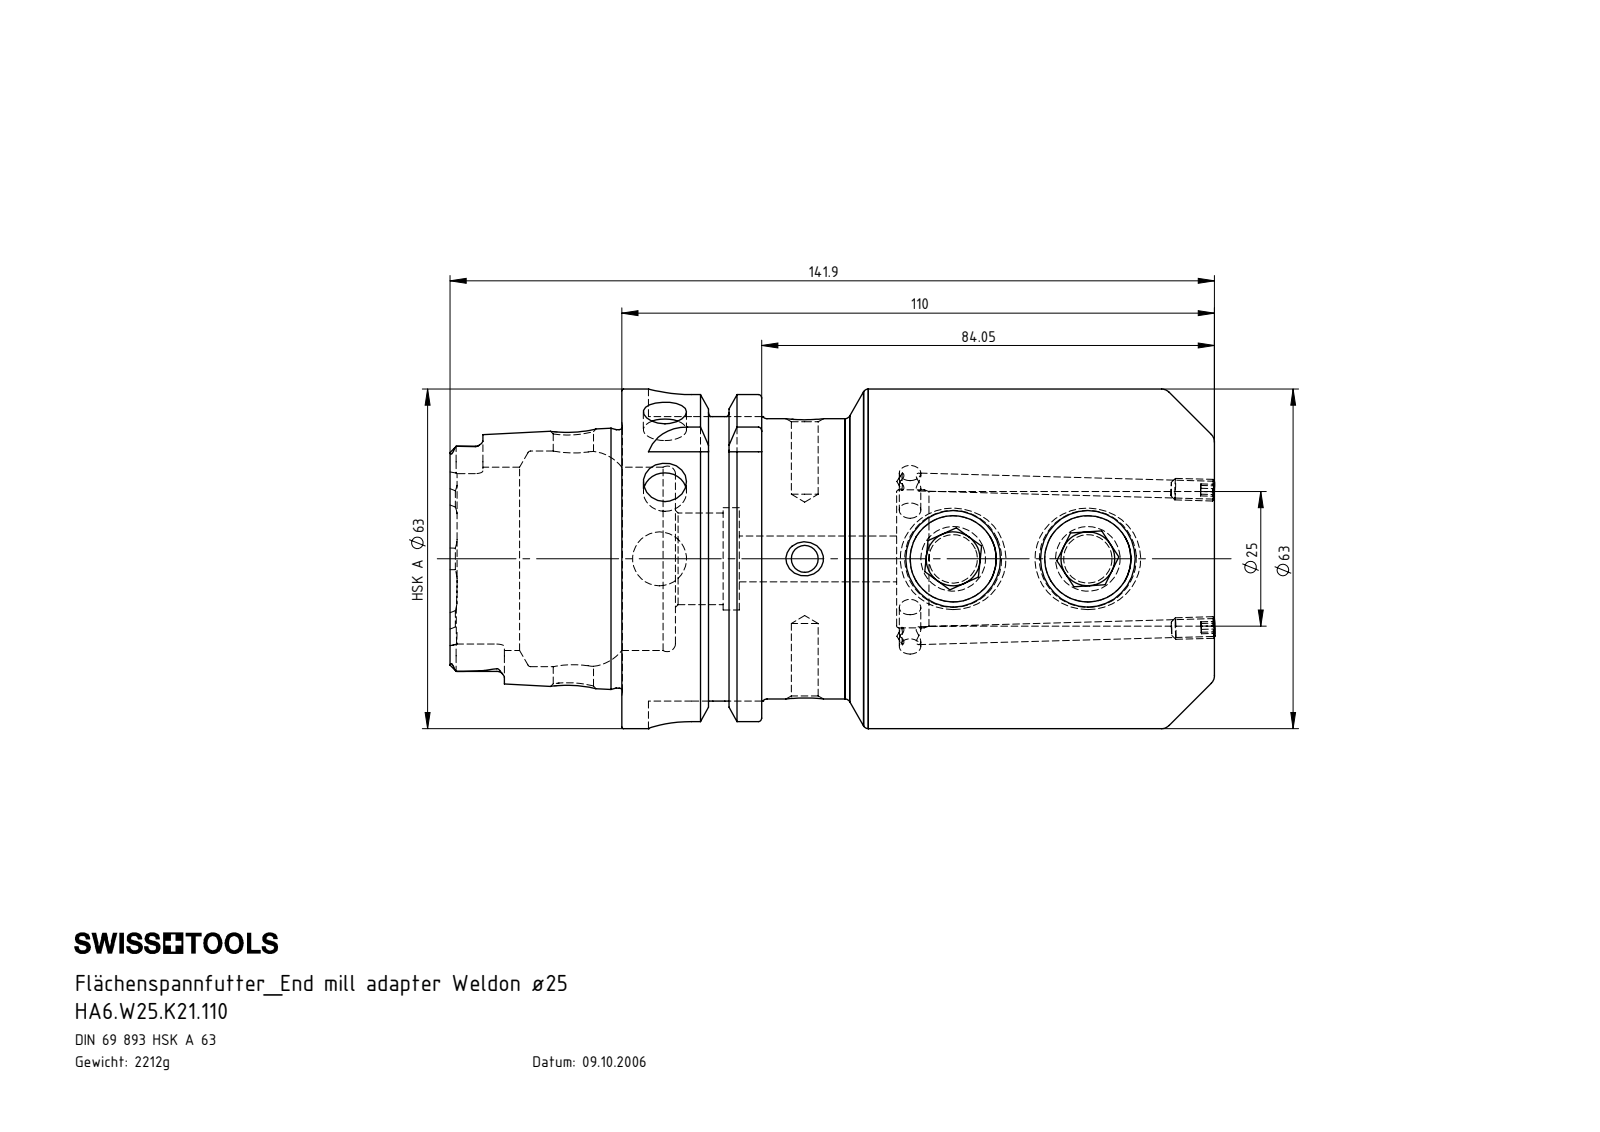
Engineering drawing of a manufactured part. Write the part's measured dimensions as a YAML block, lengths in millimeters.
part_name: "HA6.W25.K21.110; ERU-CJ3.001.008; W25-ER1.001.020; HA6-W25.K21.110_C_Fertigbearbeitung"
step_written_by: "SolidWorks 2012 (CONFIG_CONTROL_DESIGN)"
units: millimeters
bodies: {solids: 5, faces: 331, planar: 97, cylindrical: 87, other: 147}
overall_size: [142, 63, 63]
volume: 281734
surface_area: 51795
round_holes:
  - {diameter: 3.3, count: 2}
  - {diameter: 5, count: 2}
  - {diameter: 8, count: 2}
  - {diameter: 16, count: 2}
  - {diameter: 4, count: 1}
  - {diameter: 7.5, count: 1}
  - {diameter: 8.5, count: 1}
  - {diameter: 10, count: 1}
  - {diameter: 17, count: 1}
  - {diameter: 19, count: 1}
  - {diameter: 25, count: 1}
  - {diameter: 25.6, count: 1}
round_bosses_or_shafts:
  - {diameter: 18, count: 2}
  - {diameter: 4, count: 2}
  - {diameter: 63, count: 1}
  - {diameter: 54.95, count: 1}
  - {diameter: 52, count: 1}
  - {diameter: 47.94, count: 1}
partial_cylinders:
  - {radius: 1.4, count: 6}
  - {radius: 2.88, count: 4}
  - {radius: 8, count: 4}
face_to_face_distances: [110, 25.95, 84.05, 16, 9.95, 100.05, 51, 41.05, 25.05, 59]
hole_center_spacings: [25, 26.95, 27.55, 42.95, 52.55, 54.5, 79.5]
